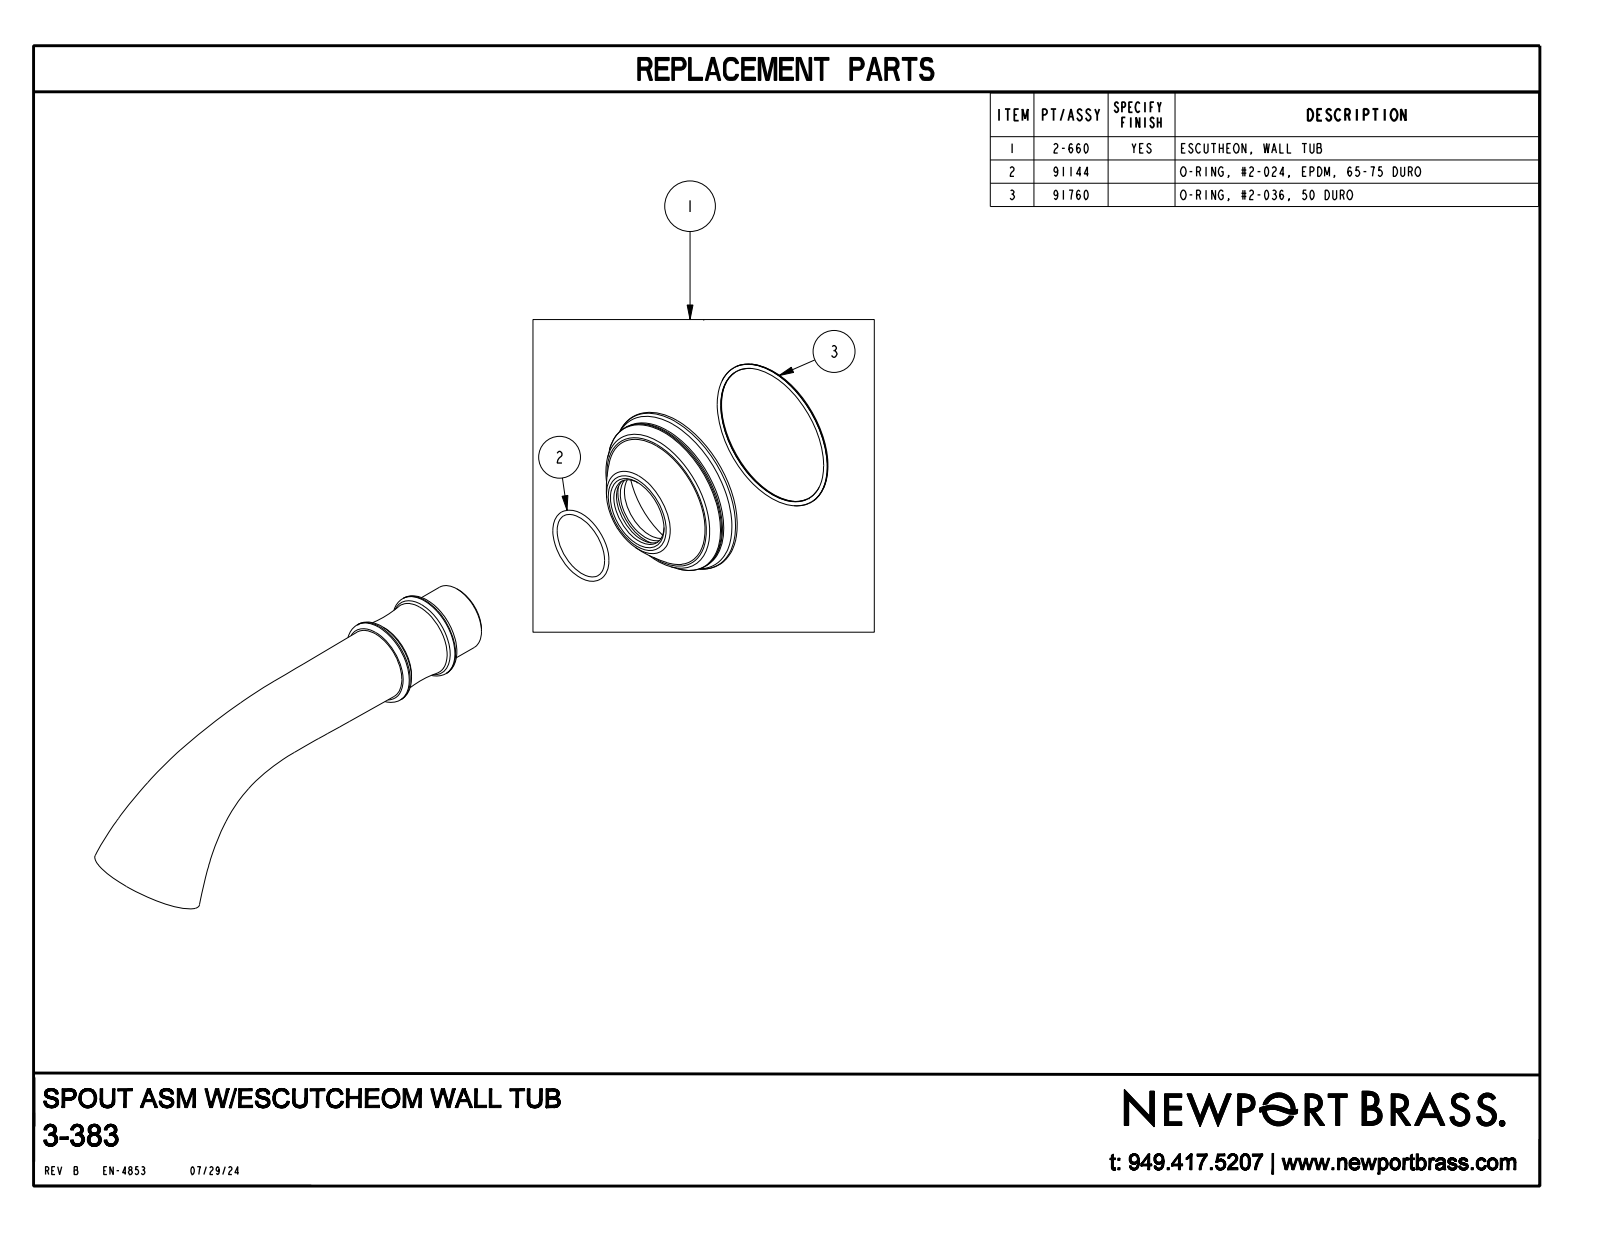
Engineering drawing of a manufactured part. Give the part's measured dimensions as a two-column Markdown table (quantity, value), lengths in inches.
| quantity | value |
| --- | --- |
| part name | 3-383_SW0001 |
| STEP written by | CREO PARAMETRIC BY PTC INC, 2018400 (AUTOMOTIVE_DESIGN) |
| units | inches |
| bodies | 1 solid, 75 faces (5 planar, 4 cylindrical, 66 other) |
| overall size | 7.825 × 3.173 × 2.771 |
| volume | 12.17 in³ |
| surface area | 44.87 in² |
| round bosses / shafts (diameter × count) | 1.4 × 1 |
| main face-to-face distances | 0.481, 0.925, 0.444, 2.125, 1.644, 1.2 |
